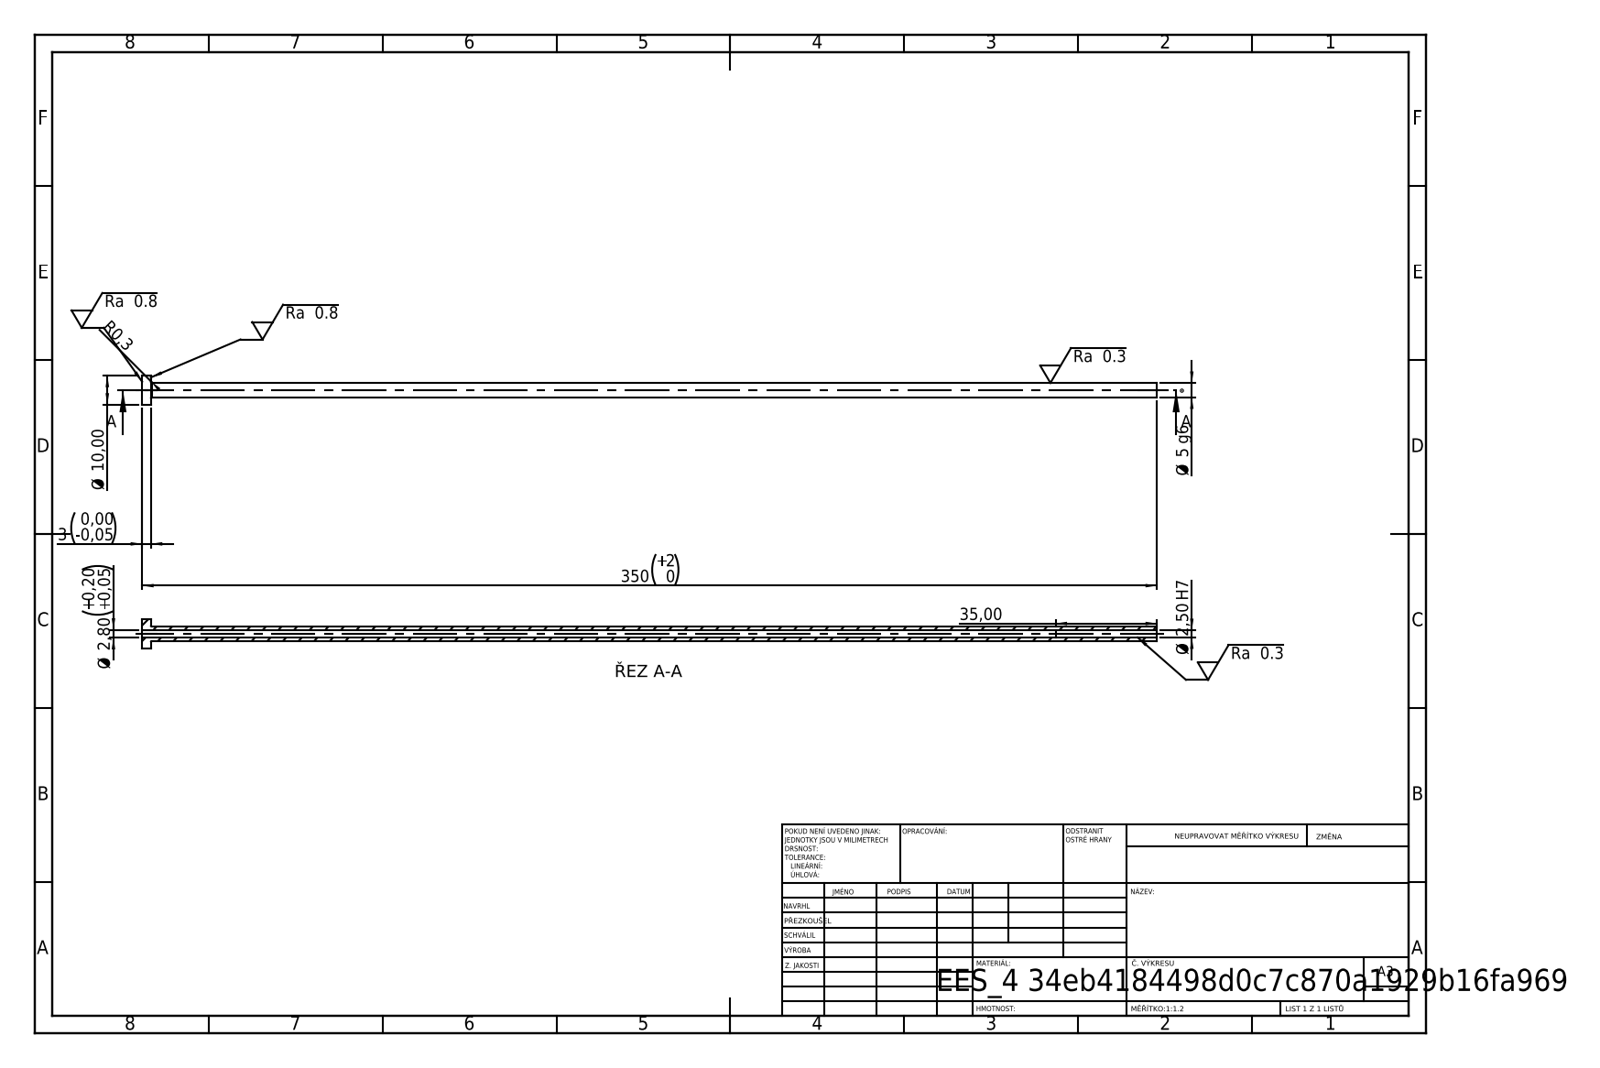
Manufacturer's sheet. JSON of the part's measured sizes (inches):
{"step_written_by": "SolidWorks 2019 (CONFIG_CONTROL_DESIGN)", "units": "inches", "bodies": {"solids": 1, "faces": 14, "planar": 4, "cylindrical": 8, "other": 2}, "overall_size": [13.78, 0.394, 0.394], "volume_in3": 0.301, "surface_area_in2": 13.54, "round_holes": [[0.098, 1], [0.11, 1]], "round_bosses_or_shafts": [[0.394, 1], [0.197, 1]], "face_to_face_distances": [0.118, 13.78, 13.661, 12.402, 12.283, 1.378]}
